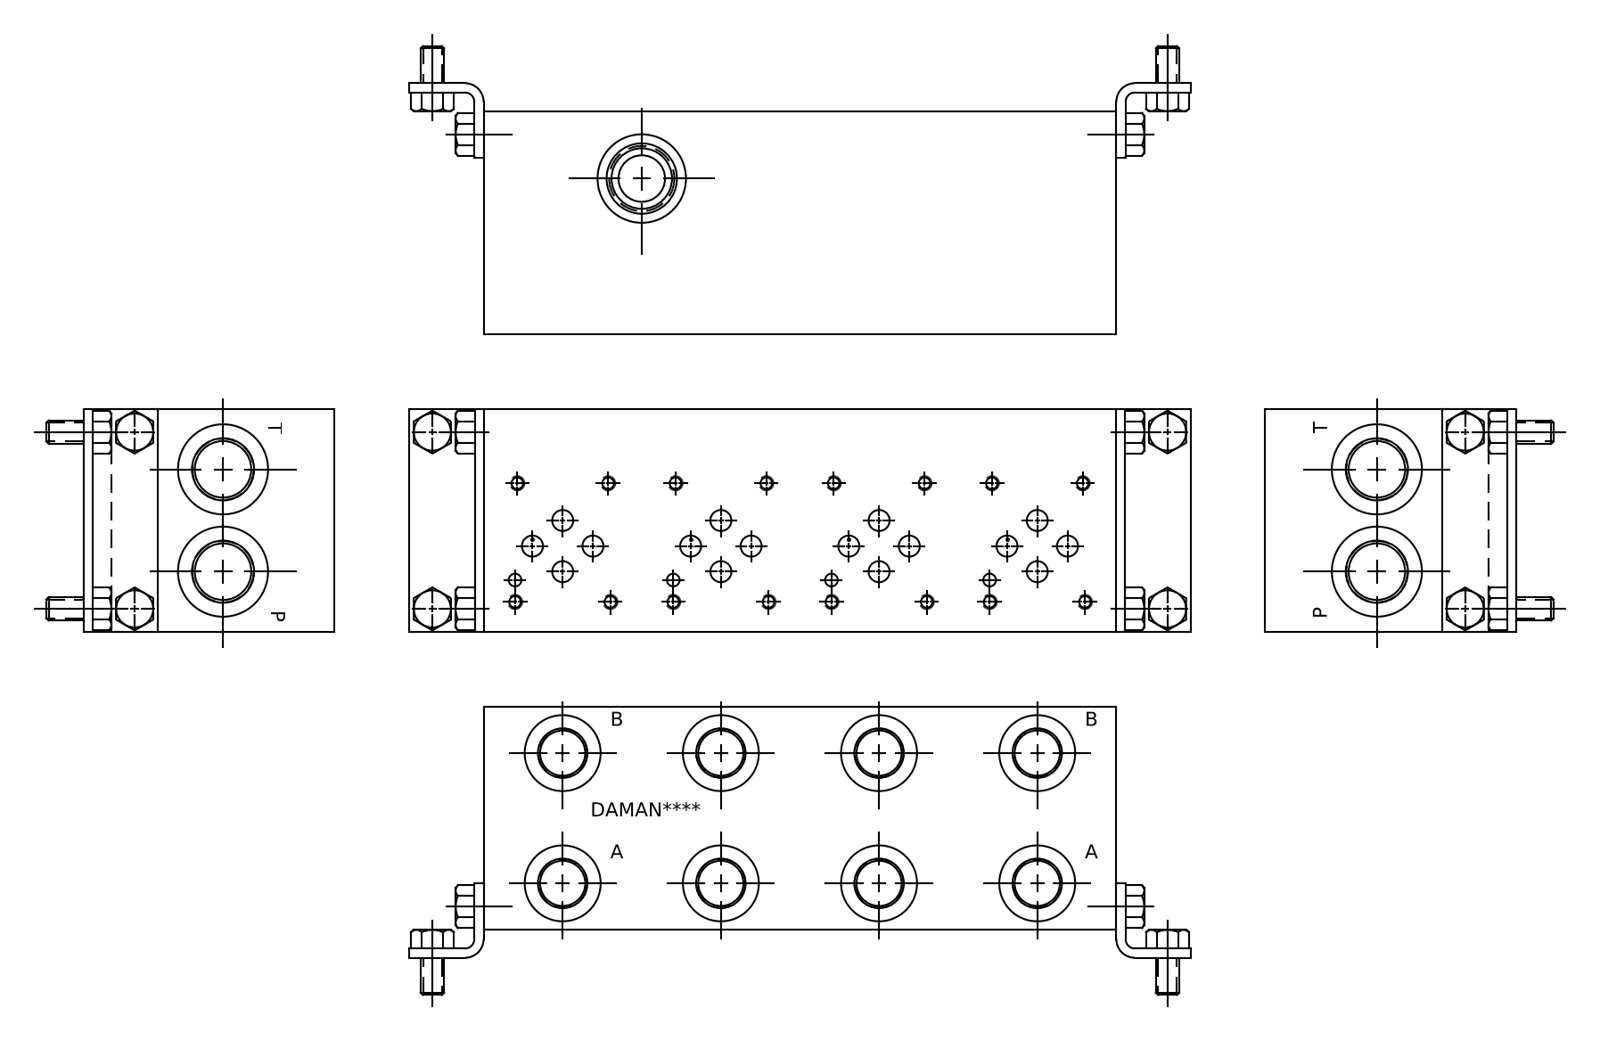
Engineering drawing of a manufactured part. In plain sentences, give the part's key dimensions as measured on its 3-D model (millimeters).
The part is named "Part_AD03P042B_C_3D". Its 3-D file was written by "Autodesk Inventor 2022 (AUTOMOTIVE_DESIGN)". It is 1 solid with 732 faces: 425 planar, 114 cylindrical and 193 other. Overall it measures 215.9 by 76.2 by 76.2 millimeters. Its volume is 1 158 000 cubic millimeters and its surface area 102 431 square millimeters. Round holes: 16 of diameter 3.78, 16 of diameter 4.83, 12 of diameter 7.14, 8 of diameter 12.7, 8 of diameter 15.06, 8 of diameter 16.76, 8 of diameter 25.93, 4 of diameter 3.96, 4 of diameter 6.35, 2 of diameter 6.53, 2 of diameter 7.92, 2 of diameter 17.48. The main face-to-face distances are 76.2, 215.9, 0.79, 75.41, 215.11, 214.32, 13.77, 12.98, 62.43, 17.37. The hole center spacings are 107.95, 53.98, 53.97, 161.93, 19.95, 22.05, 33.55, 51.45.
